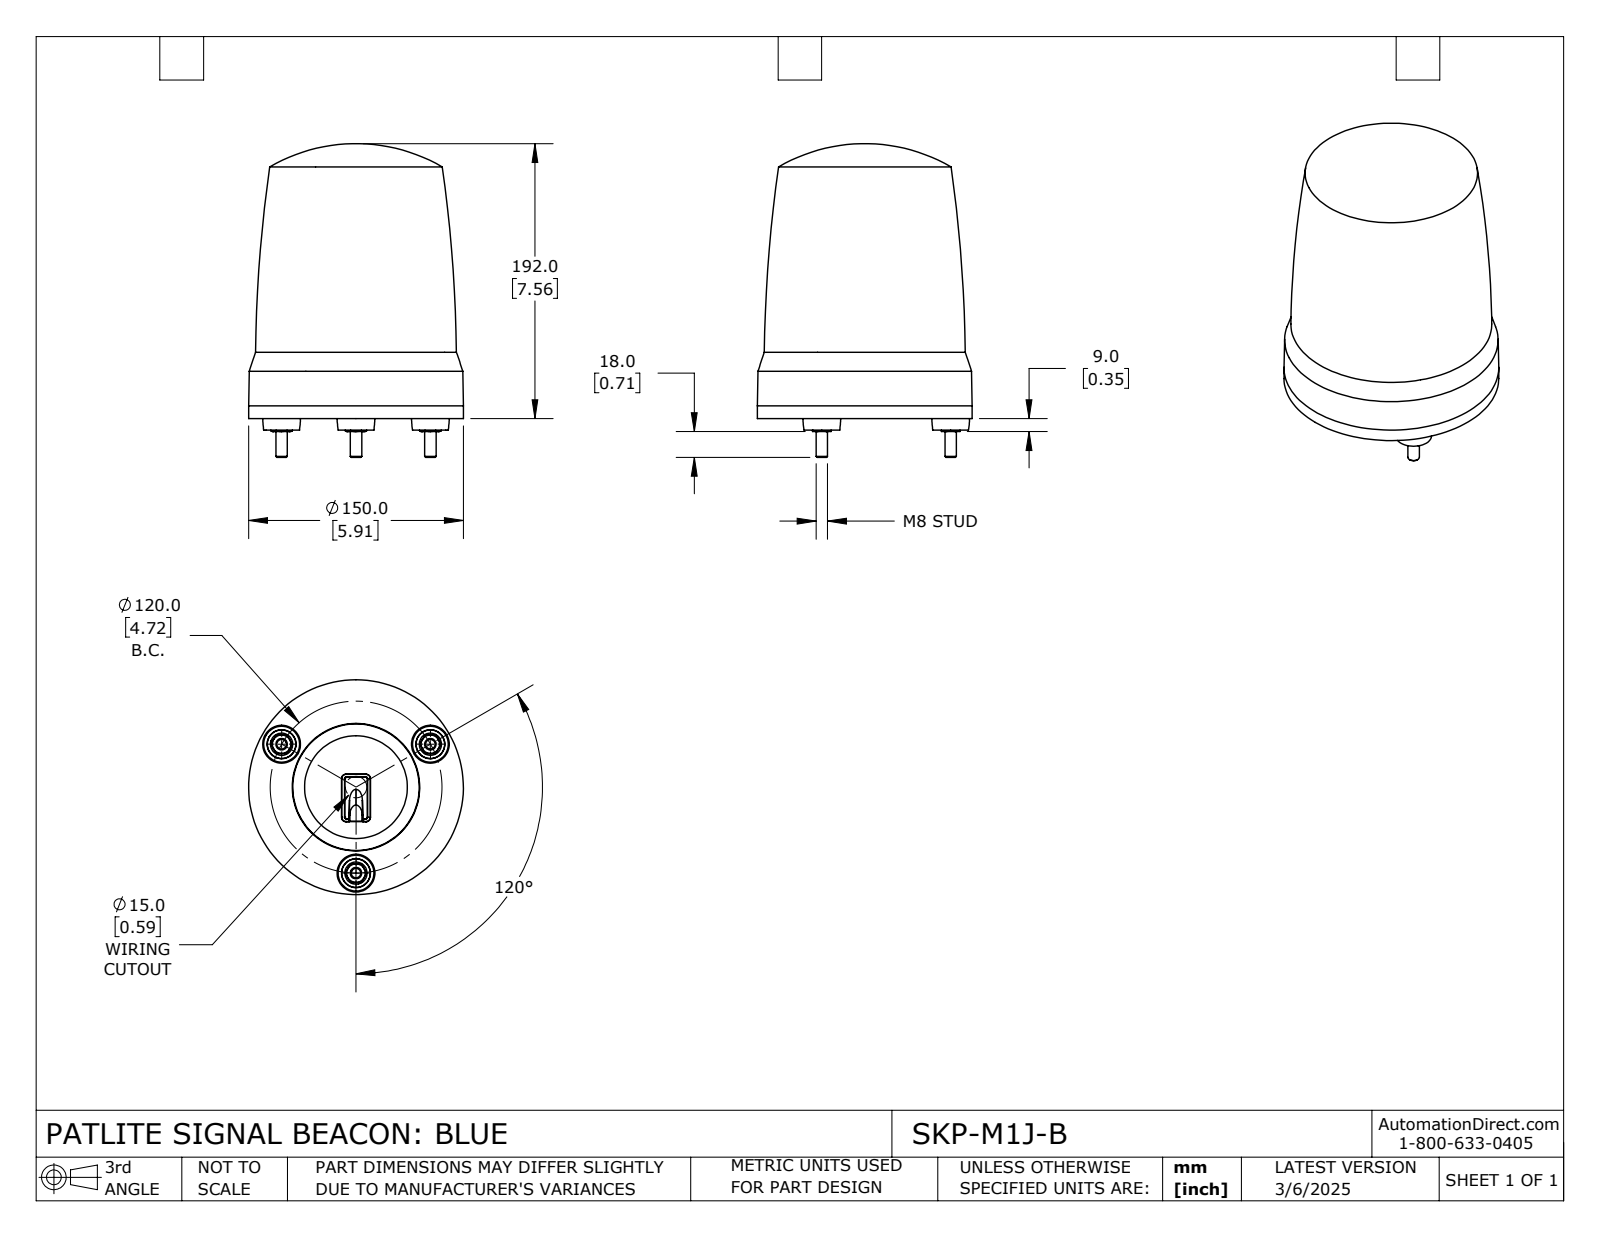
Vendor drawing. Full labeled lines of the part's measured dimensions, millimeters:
Part name (STEP PRODUCT): SKP-M1J-B
STEP written by: SolidWorks 2024 (CONFIG_CONTROL_DESIGN)
Units: millimetres
Bodies: 1 solid, 144 faces (49 planar, 14 cylindrical, 81 other)
Overall size (bounding box): 219 × 150 × 150
Volume: 2 538 000 mm³ · Surface area: 119 026 mm²
Round bosses / shafts (diameter × count): ⌀15.5 ×3, ⌀8 ×3, ⌀150 ×1
Main face-to-face distances: 32.7, 8, 40.7, 13, 7.1, 0.9, 33.6, 1.6, 36.05, 41.55
